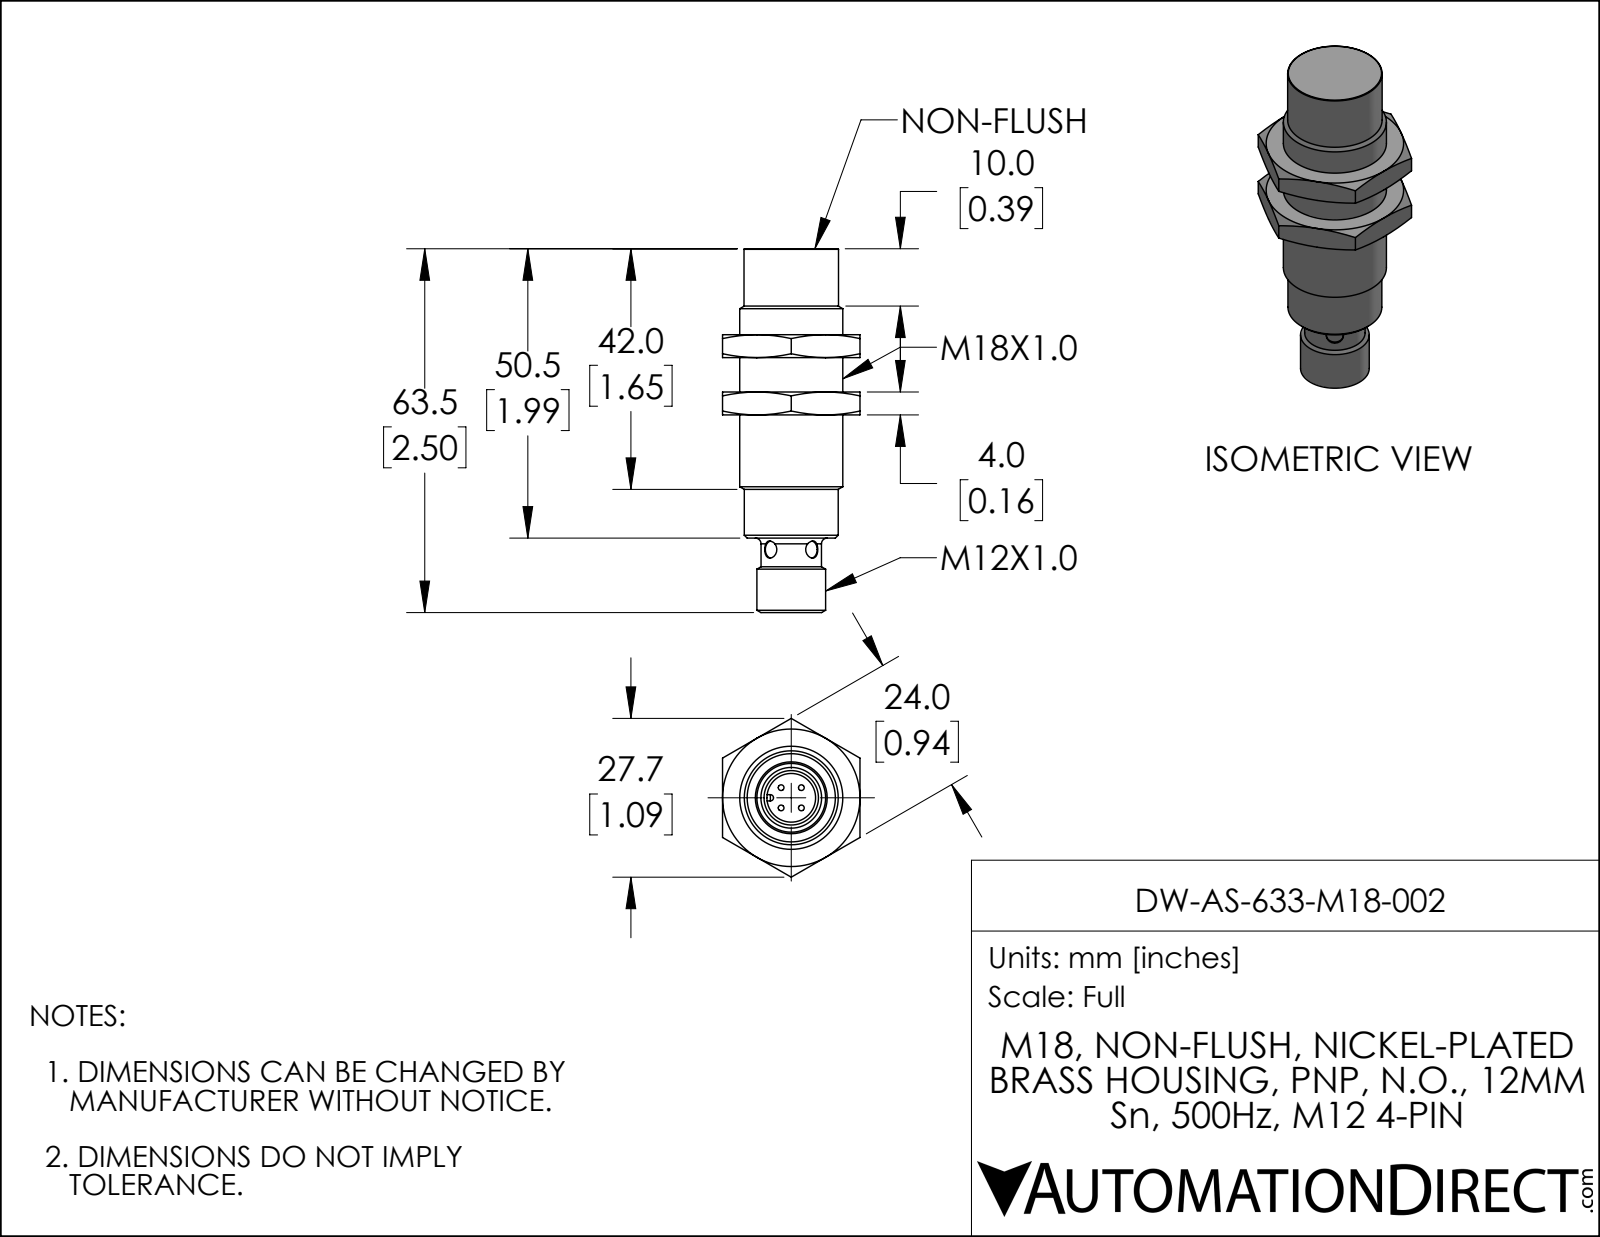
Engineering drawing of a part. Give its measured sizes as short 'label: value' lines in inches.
name: DW-AS-633-M18-002
written by: SolidWorks 2019 (AUTOMOTIVE_DESIGN)
unit: in
bodies: 1 solid, 82 faces (27 planar, 18 cylindrical, 37 other)
size: 2.5 × 1.091 × 0.945
volume: 0.905 in³; area: 8.001 in²
holes: 2× ⌀0.118, 1× ⌀0.335
bosses: 4× ⌀0.039, 1× ⌀0.709, 1× ⌀0.65, 1× ⌀0.646, 1× ⌀0.472, 1× ⌀0.415
rounds: 2× R0.022
face distances: 0.394, 0.157, 0.945, 0.591, 0.748, 0.984, 1.142, 0.551, 0.236, 1.988
